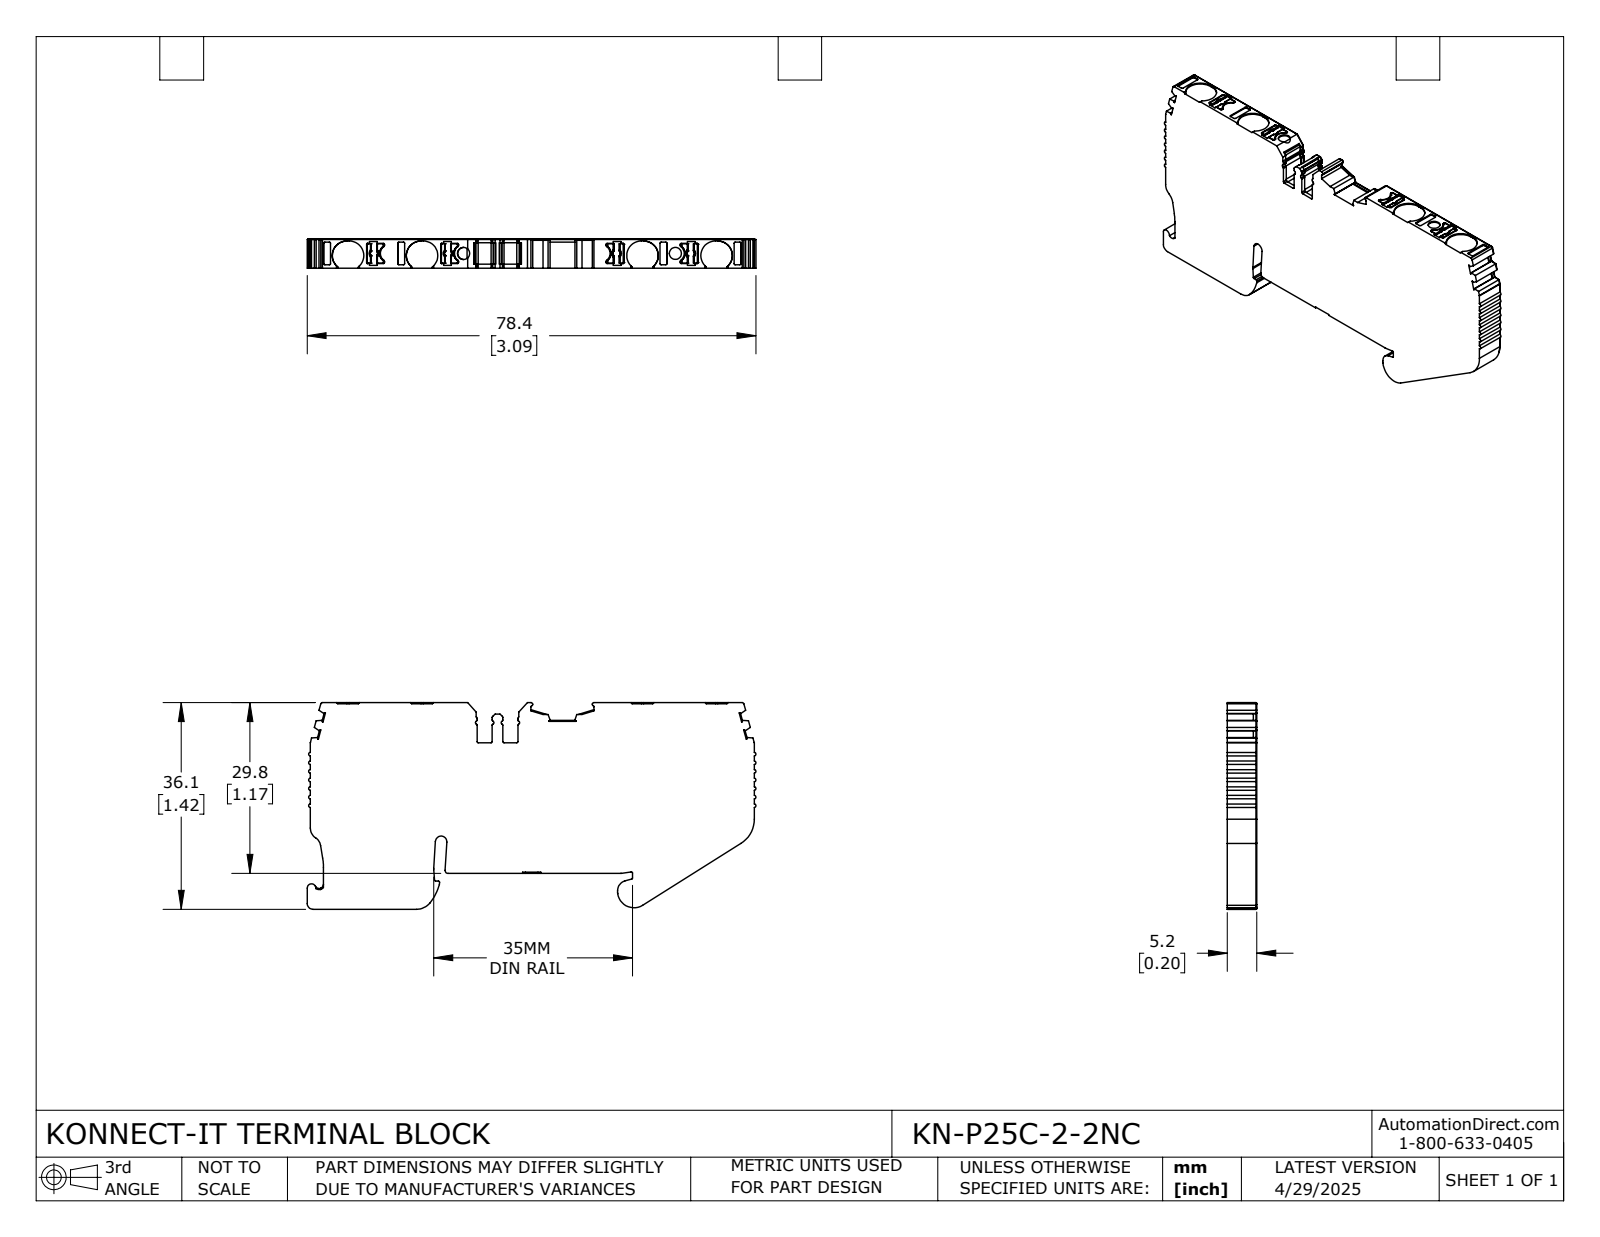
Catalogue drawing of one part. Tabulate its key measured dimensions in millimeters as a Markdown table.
| quantity | value |
| --- | --- |
| part name | KN-P25C-2-2NC |
| STEP written by | SolidWorks 2024 (CONFIG_CONTROL_DESIGN) |
| units | millimeters |
| bodies | 1 solid, 739 faces (381 planar, 291 cylindrical, 67 other) |
| overall size | 78.36 × 36.07 × 5.15 |
| volume | 11 972 mm³ |
| surface area | 6 218 mm² |
| round holes (diameter × count) | 2.1 × 2 |
| partial cylindrical surfaces (radius × count) | 0.2 × 78, 0.3 × 39, 0.1 × 21, 0.5 × 18, 0.15 × 16, 0.4 × 9, 2.55 × 8, 1.5 × 4 |
| main face-to-face distances | 5.15, 29.61, 29.81, 6.26, 35.87, 36.07, 77.52, 1.2, 5, 4.5 |
| hole center spacings | 36.98 |
